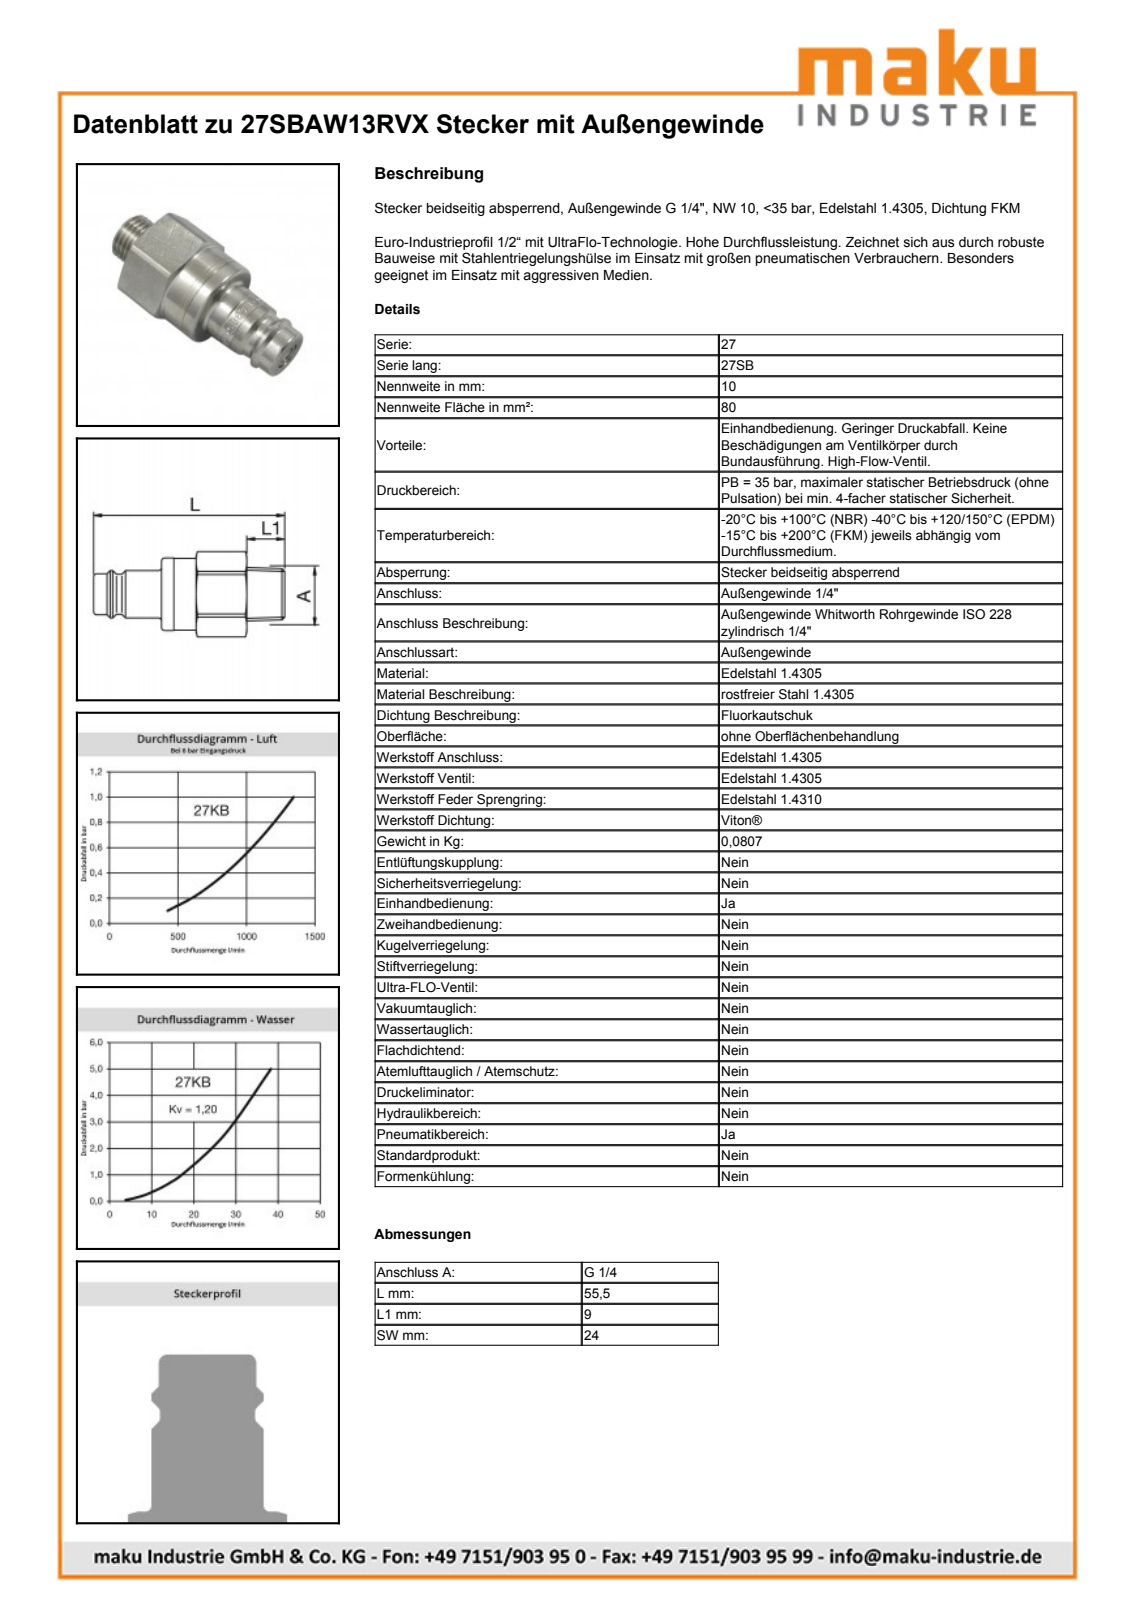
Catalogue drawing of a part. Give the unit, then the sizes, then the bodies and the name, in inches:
Units: inches
Overall size (bounding box): 2.181 × 1.046 × 1.033
Round holes (diameter × count): ⌀0.748 ×1, ⌀0.799 ×1
Round bosses / shafts (diameter × count): ⌀0.906 ×1, ⌀0.898 ×1, ⌀0.743 ×1, ⌀0.728 ×1, ⌀0.591 ×1, ⌀0.571 ×1, ⌀0.518 ×1, ⌀0.512 ×1
Partial cylindrical surfaces — rounded edges, fillets, slot ends (radius × count): R0.281 ×1, R0.533 ×1
Main face-to-face distances: 0.945, 0.98, 1.335, 0.354, 0.846, 1.827, 2.181, 1, 0.154, 0.827
Volume: 0.97 in³ · Surface area: 7.693 in²
Bodies: 1 solid, 245 faces (99 planar, 42 cylindrical, 104 other)
Part name (STEP PRODUCT): D107965
STEP written by: Autodesk Inventor 2013 (AUTOMOTIVE_DESIGN)
